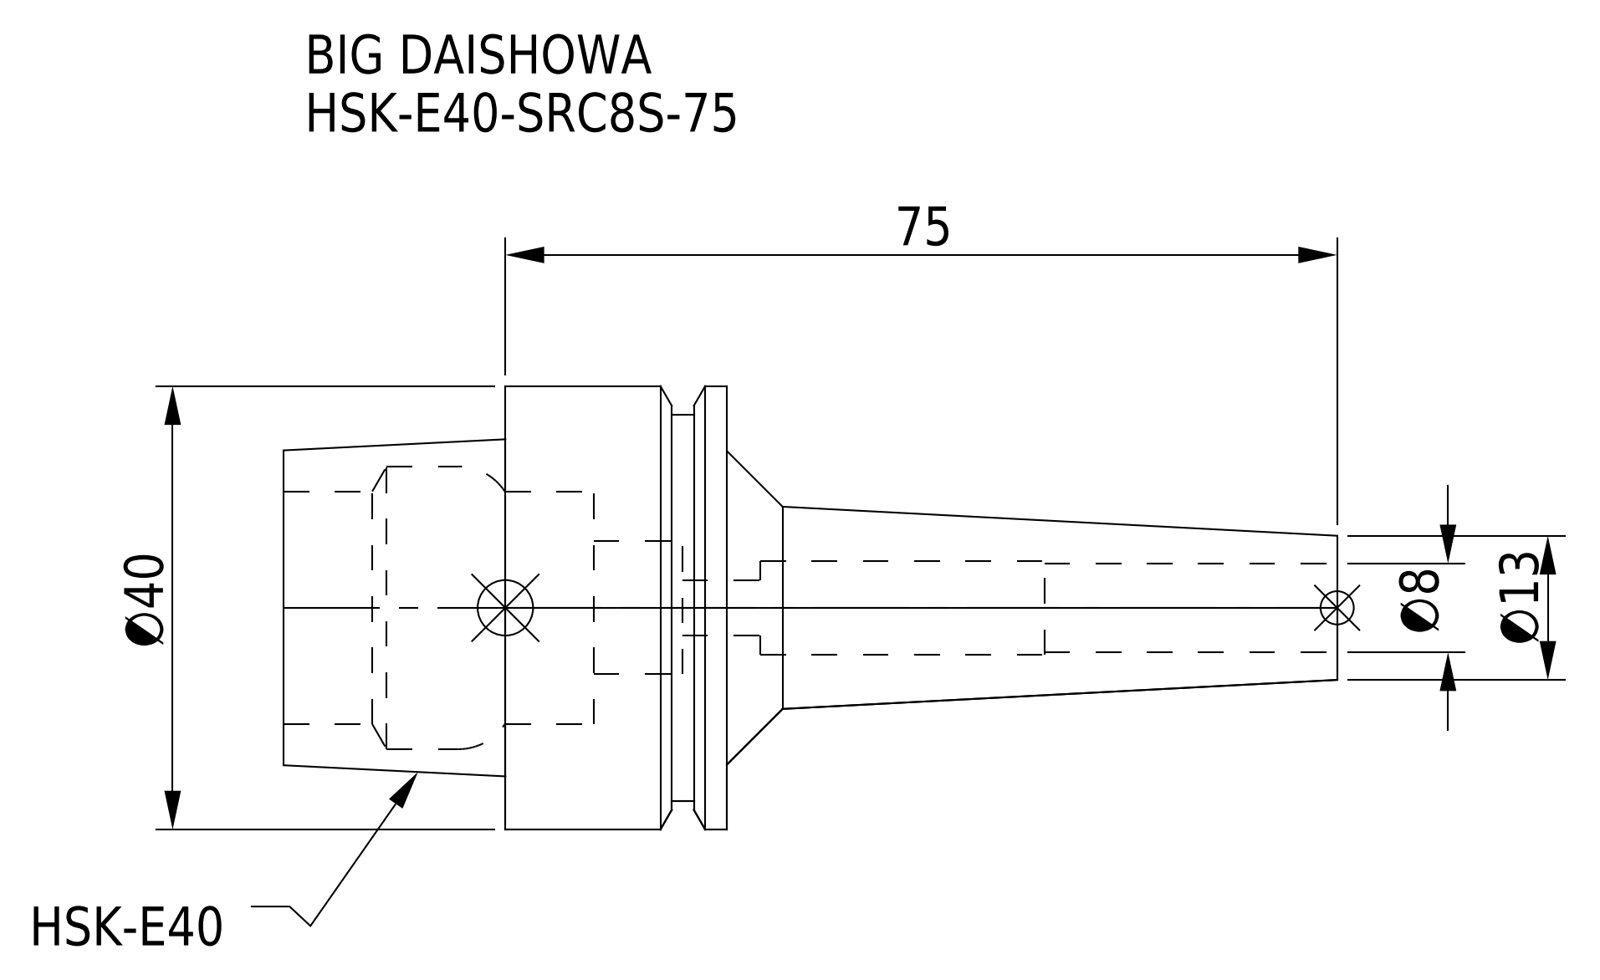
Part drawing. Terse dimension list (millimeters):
name: HSK-E40-SRC8S-75
written by: CREO PARAMETRIC BY PTC INC, 2016380 (AUTOMOTIVE_DESIGN)
unit: mm
bodies: 1 solid, 46 faces (10 planar, 22 cylindrical, 14 other)
size: 95 × 40 × 40
volume: 34 564 mm³; area: 13 520 mm²
holes: 1× ⌀5, 1× ⌀8, 1× ⌀8.5, 1× ⌀12, 1× ⌀21, 1× ⌀25.5
bosses: 1× ⌀40, 1× ⌀34.8
face distances: 20, 40, 12.05, 7.95, 27.95, 8, 7.05, 3, 4.05, 15.95
